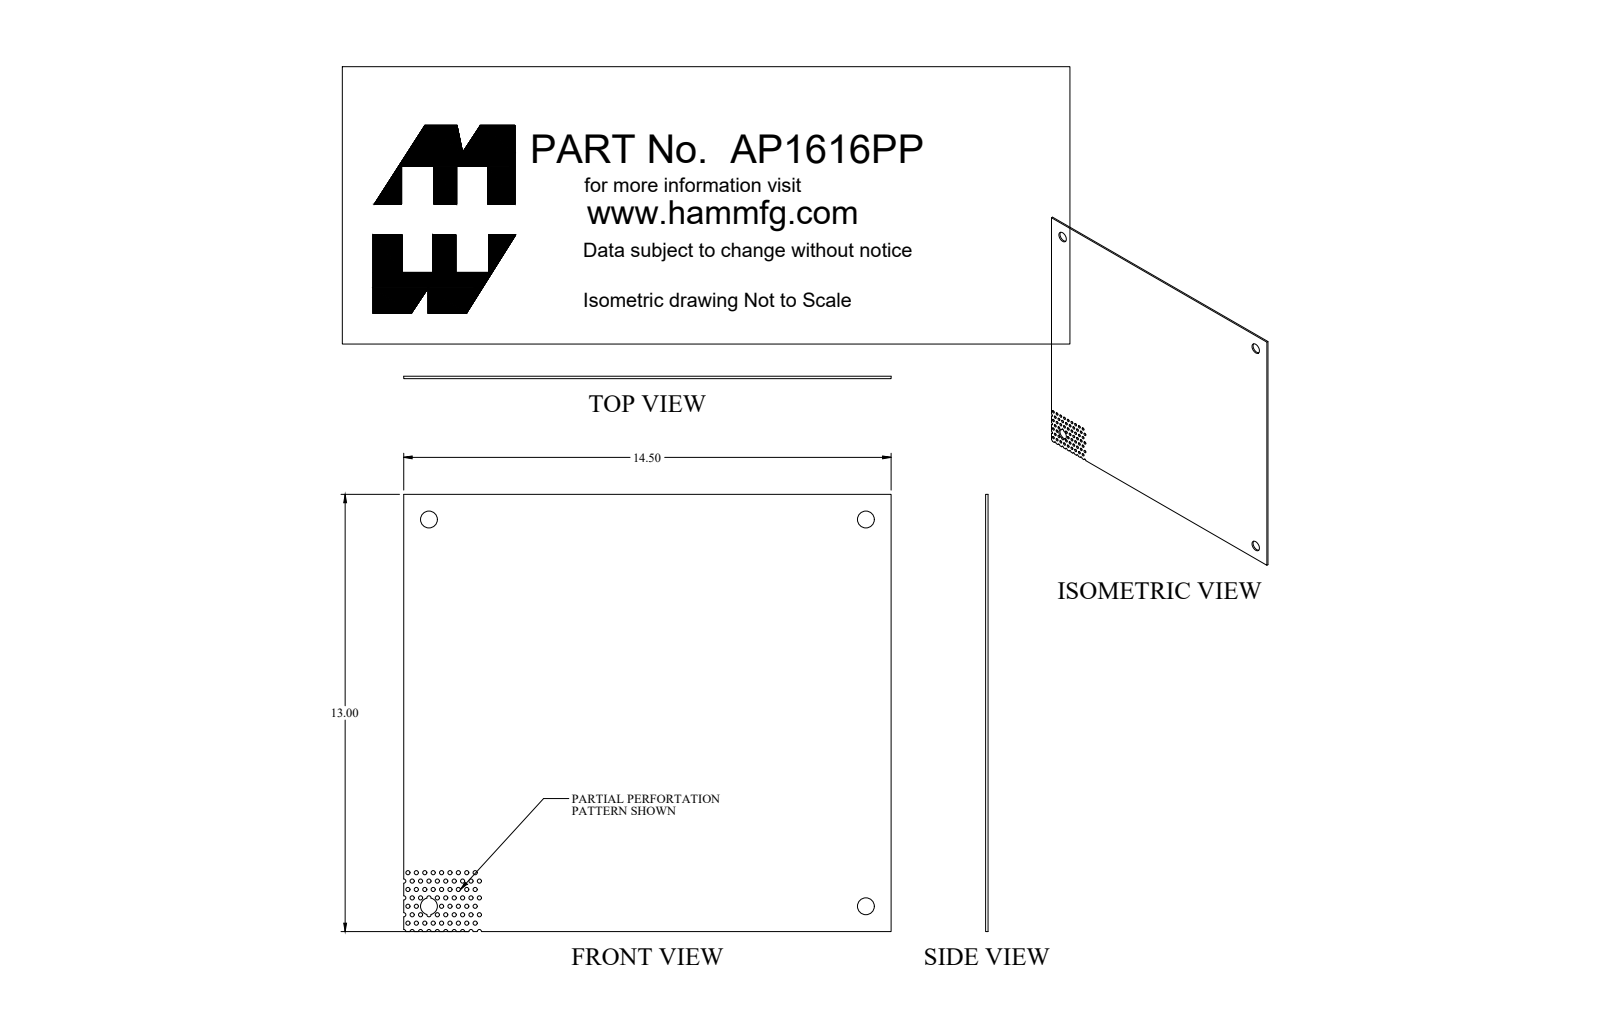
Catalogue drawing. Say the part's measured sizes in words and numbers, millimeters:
The part is named "AP1616PP_Default". Its 3-D file was written by "SolidWorks 2019 (CONFIG_CONTROL_DESIGN)". It is 1 solid with 169 faces: 18 planar, 151 cylindrical and 0 other. Overall it measures 368.3 by 330.2 by 1.8 millimeters. Its volume is 220 600 cubic millimeters and its surface area 245 200 square millimeters. Round holes: 50 of diameter 3.2, 9 of diameter 3.2, 4 of diameter 12.7. Partial cylindrical surfaces (rounded edges, fillets, slot ends): 15 of radius 1.6. The main face-to-face distances are 1.8, 330.2, 368.3. The hole center spacings are 7.1, 12.7, 6.4, 17.1, 23.1, 11.4, 14.2, 29.3.
